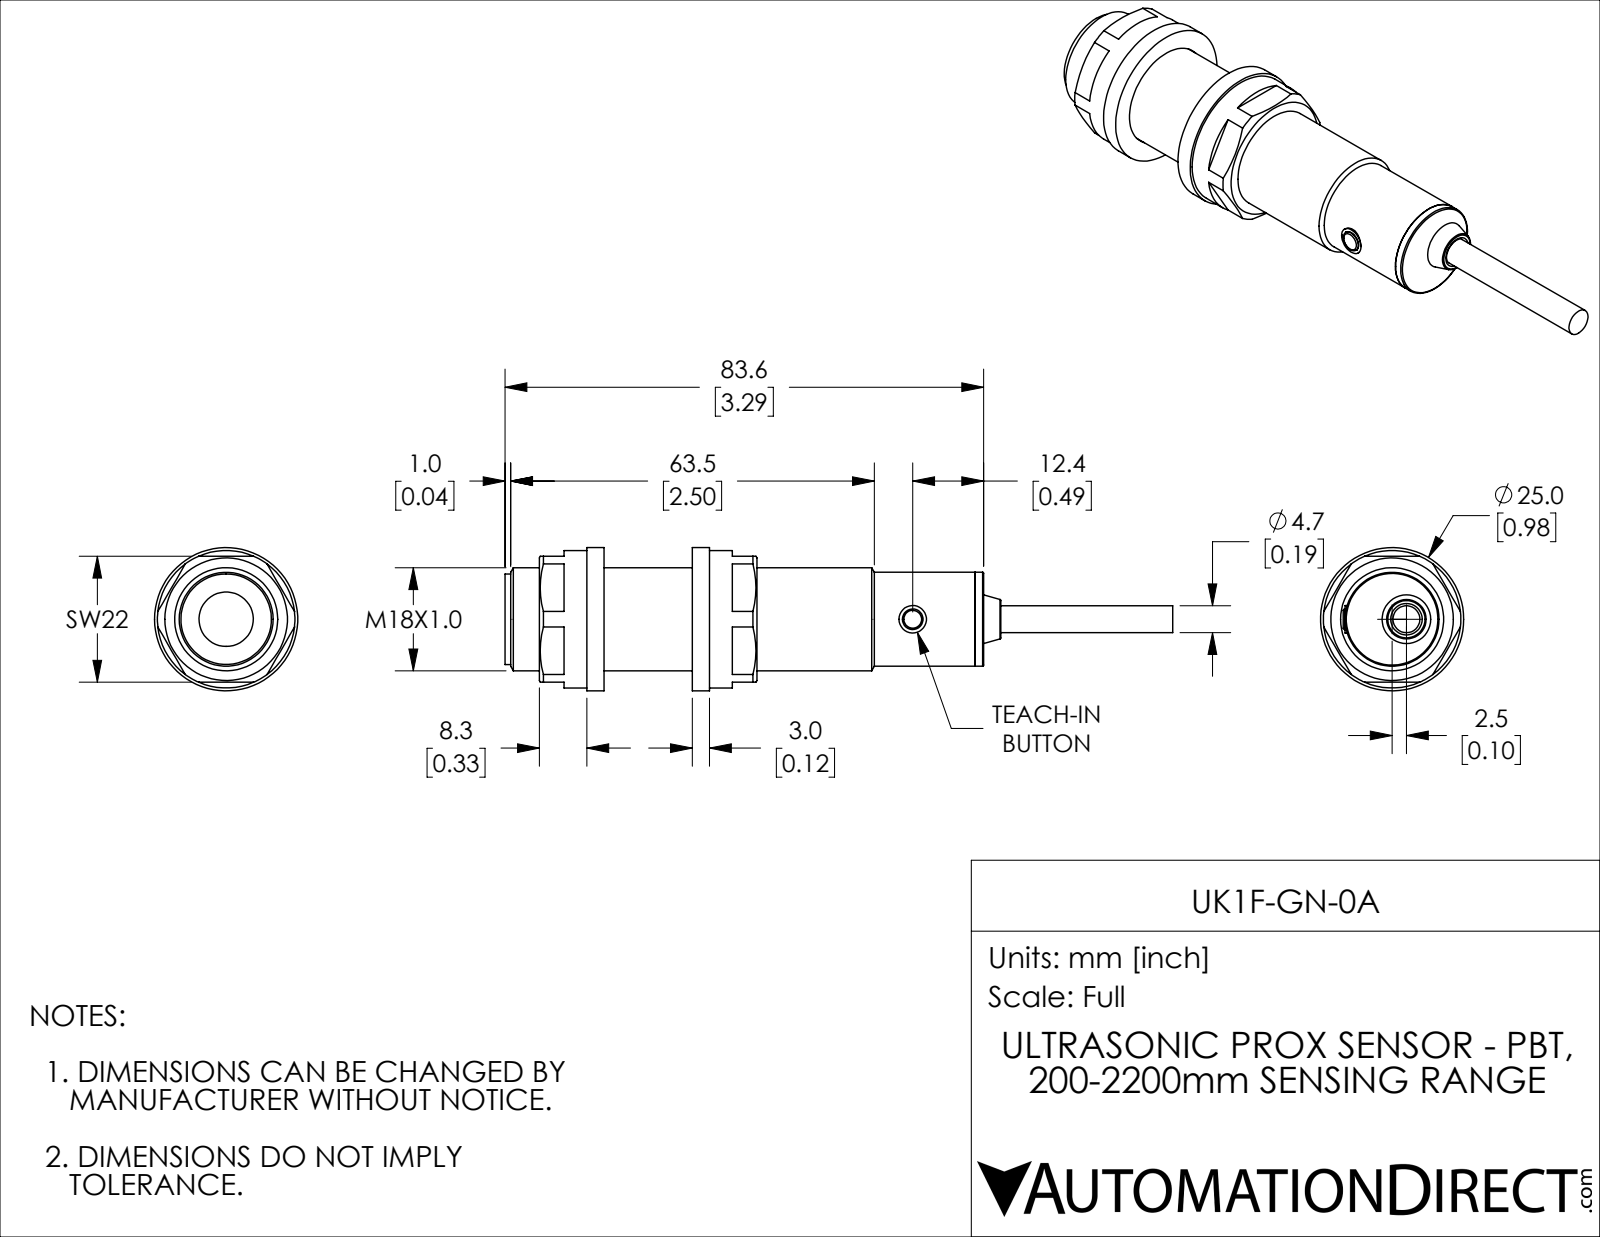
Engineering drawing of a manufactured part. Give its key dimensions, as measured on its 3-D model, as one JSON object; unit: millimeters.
{"part_name": "UK1F-GN-0A", "step_written_by": "SolidWorks 2018 (AUTOMOTIVE_DESIGN)", "units": "millimeters", "bodies": {"solids": 10, "faces": 107, "planar": 49, "cylindrical": 40, "other": 18}, "overall_size": [116.6, 25, 25], "volume_mm3": 25220, "surface_area_mm2": 11419, "round_holes": [[4.7, 2], [3.6, 1], [9.5, 1], [18, 1], [18.2, 1]], "round_bosses_or_shafts": [[25, 1], [24, 1], [16.4, 1], [15.8, 1], [5.4, 1], [4.8, 1]], "face_to_face_distances": [3, 18.4, 21.4, 67.8, 46.4, 13.3, 34.7, 81.1, 16.3, 64.8], "hole_center_spacings": [2.5]}
